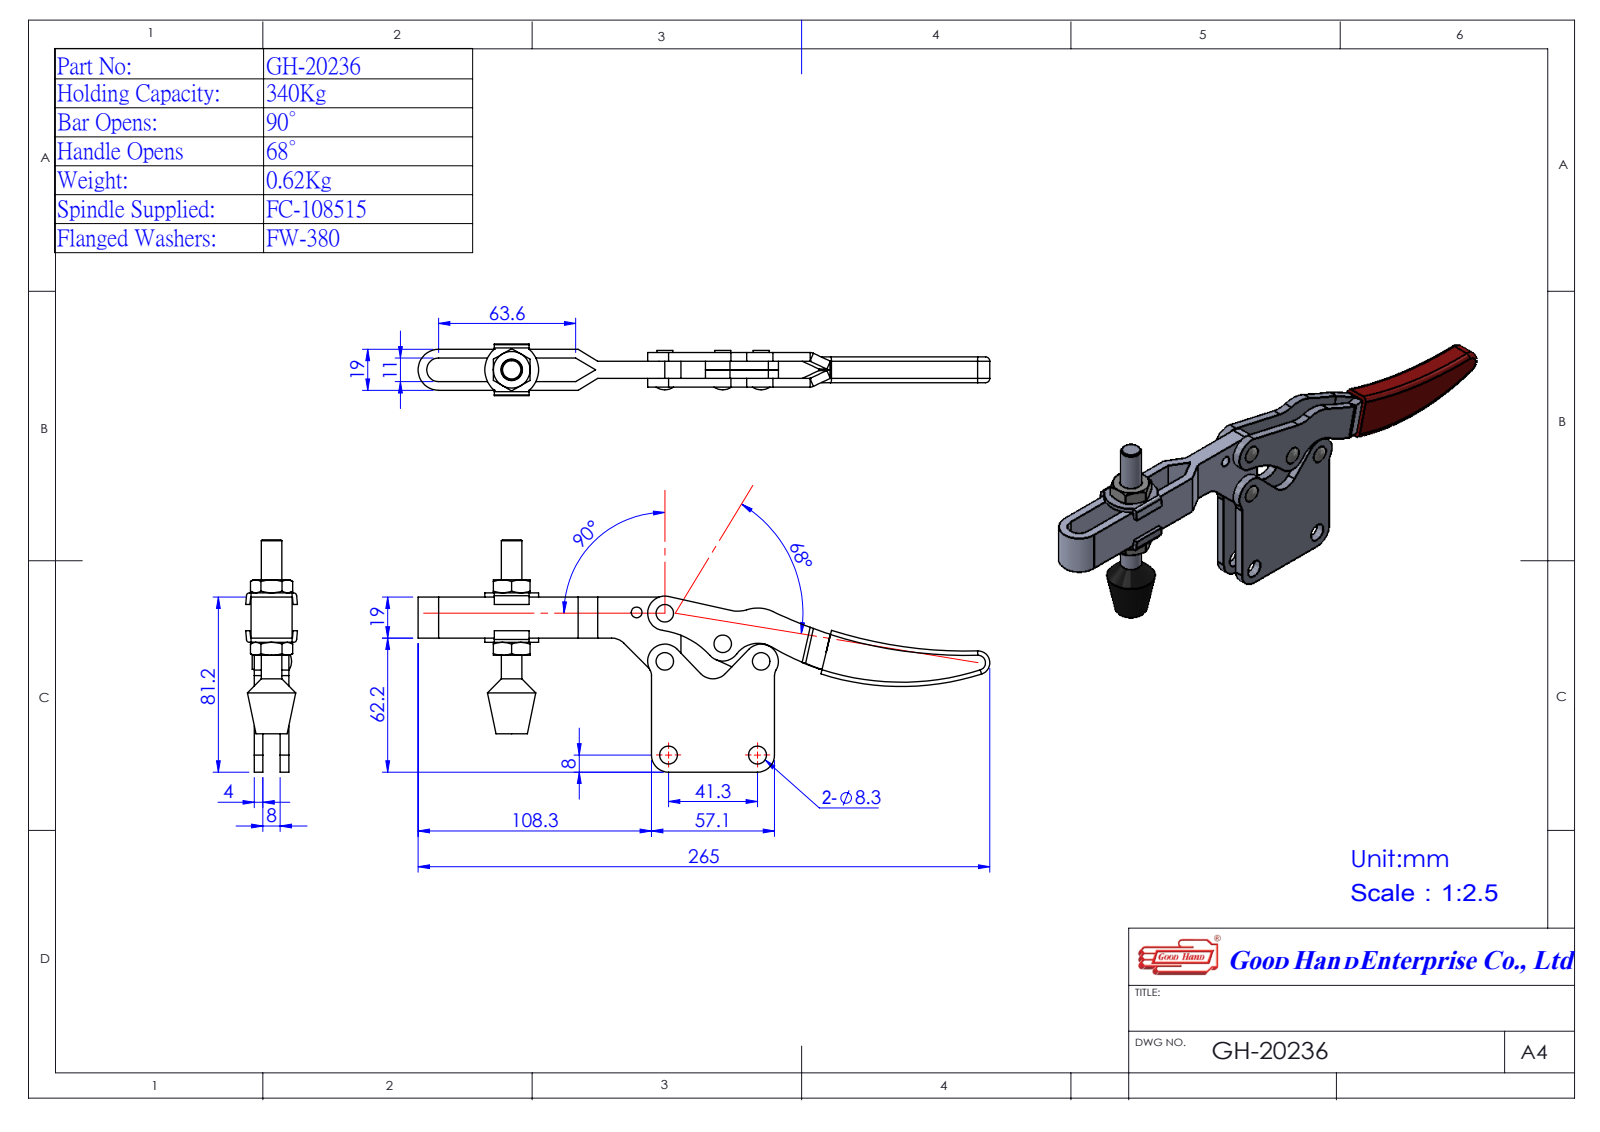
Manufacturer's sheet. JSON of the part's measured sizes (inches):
{"part_name": "GH-20236(簡化)-1; 12023508-1^GH-20236(簡化)-1; Group6^GH-20236(簡化)-1; Group3^GH-20236(簡化)-1 (+2 more)", "step_written_by": "SolidWorks 2016 (AUTOMOTIVE_DESIGN)", "units": "inches", "bodies": {"solids": 5, "faces": 259, "planar": 101, "cylindrical": 112, "other": 46}, "overall_size": [10.416, 4.244, 0.946], "volume_in3": 5.541, "surface_area_in2": 74.25, "round_holes": [[0.197, 4], [0.327, 2]], "round_bosses_or_shafts": [[0.289, 4], [0.197, 3], [0.25, 2], [0.375, 1]], "partial_cylinders_radius": [[0.315, 6], [0.197, 4], [0.295, 2], [0.313, 2], [0.079, 1], [0.11, 1], [0.217, 1], [0.374, 1]], "face_to_face_distances": [0.157, 0.315, 0.472, 0.531, 0.059, 0.374, 0.217, 0.098, 0.63, 0.591], "hole_center_spacings": [1.712, 2.407, 0.772, 0.878, 1.102, 1.196, 1.626, 1.76]}
